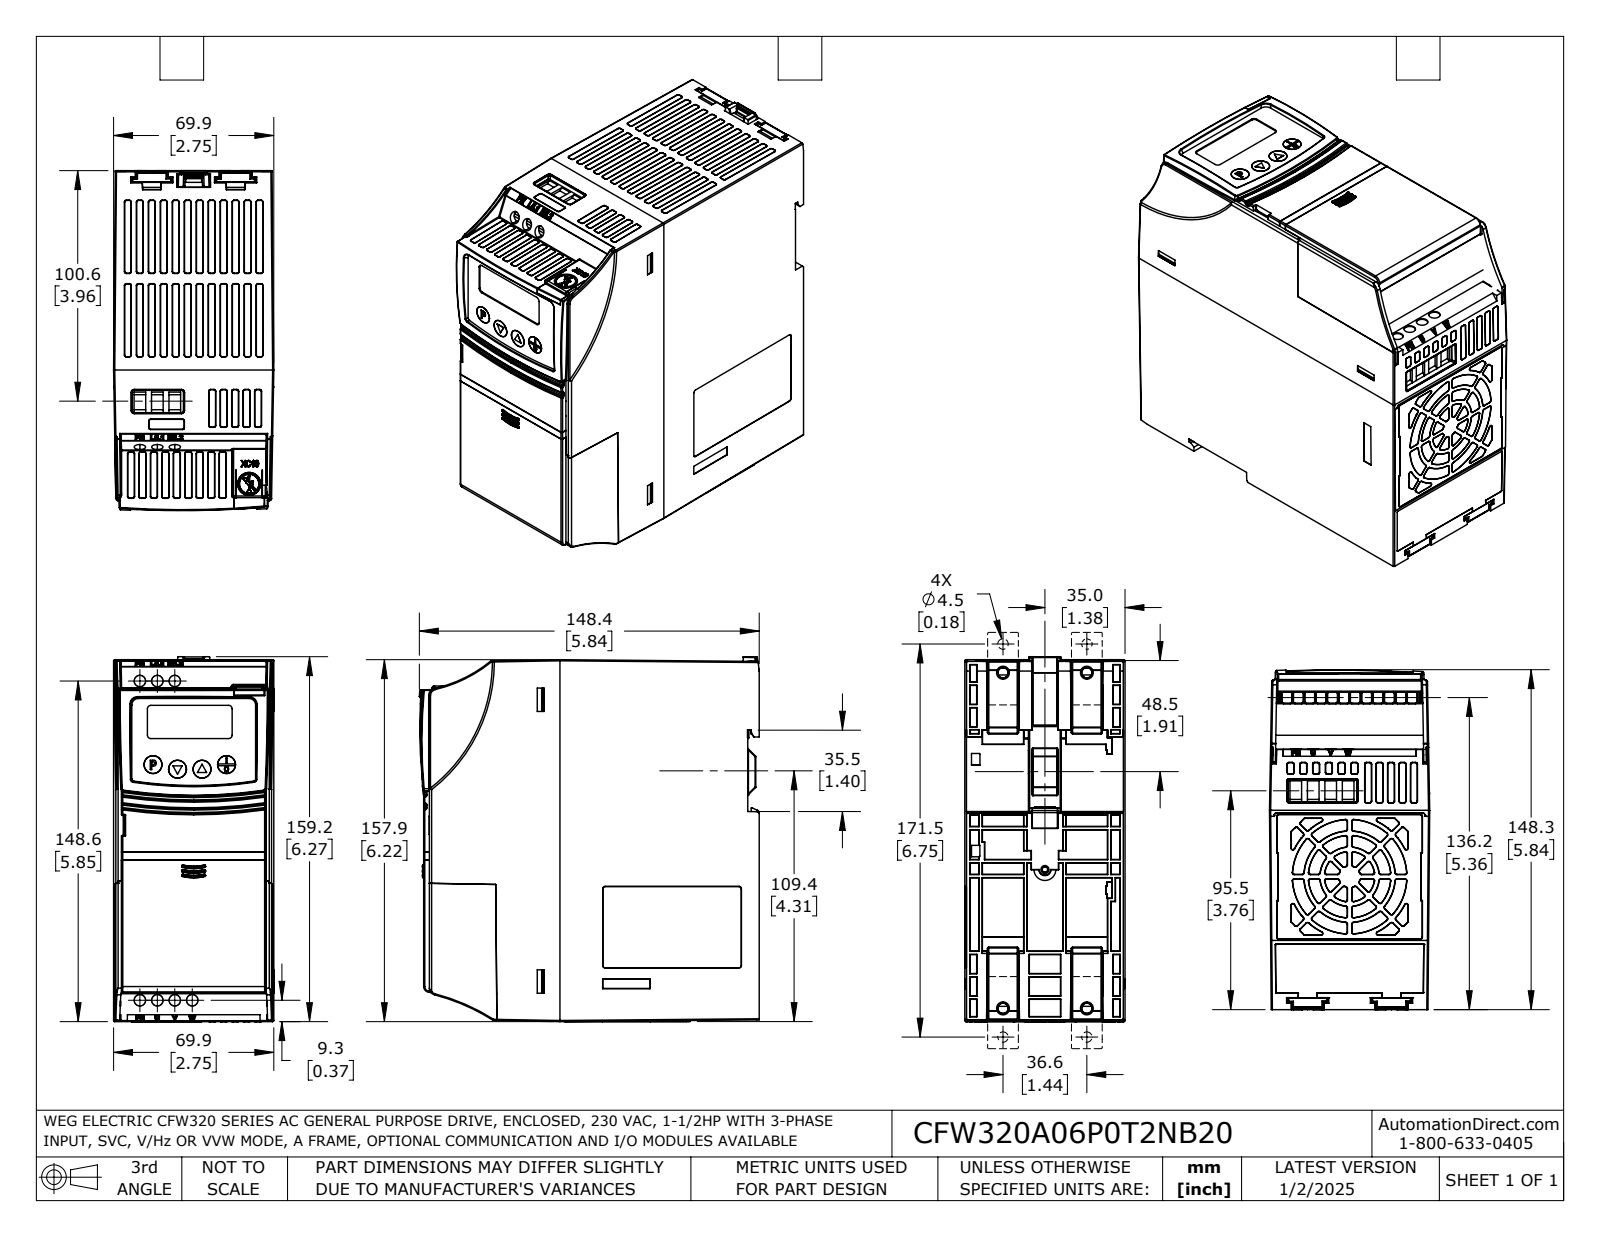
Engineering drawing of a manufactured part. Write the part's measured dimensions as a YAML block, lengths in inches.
part_name: "CFW320A06P0T2NB20"
step_written_by: "SolidWorks 2021 (AUTOMOTIVE_DESIGN)"
units: inches
bodies: {solids: 6, faces: 3715, planar: 1587, cylindrical: 853, other: 1275}
overall_size: [6.269, 5.841, 2.754]
volume: 15.24
surface_area: 309
round_holes:
  - {diameter: 0.197, count: 3}
partial_cylinders:
  - {radius: 0.012, count: 327}
  - {radius: 0.02, count: 150}
  - {radius: 0.039, count: 13}
  - {radius: 0.03, count: 5}
  - {radius: 0.118, count: 3}
  - {radius: 0.01, count: 2}
  - {radius: 0.098, count: 1}
  - {radius: 0.126, count: 1}
face_to_face_distances: [0.07, 0.055, 0.019, 0.05, 6, 5.33, 5.275, 5.571, 5.516, 0.241]
hole_center_spacings: [0.3, 0.6]
